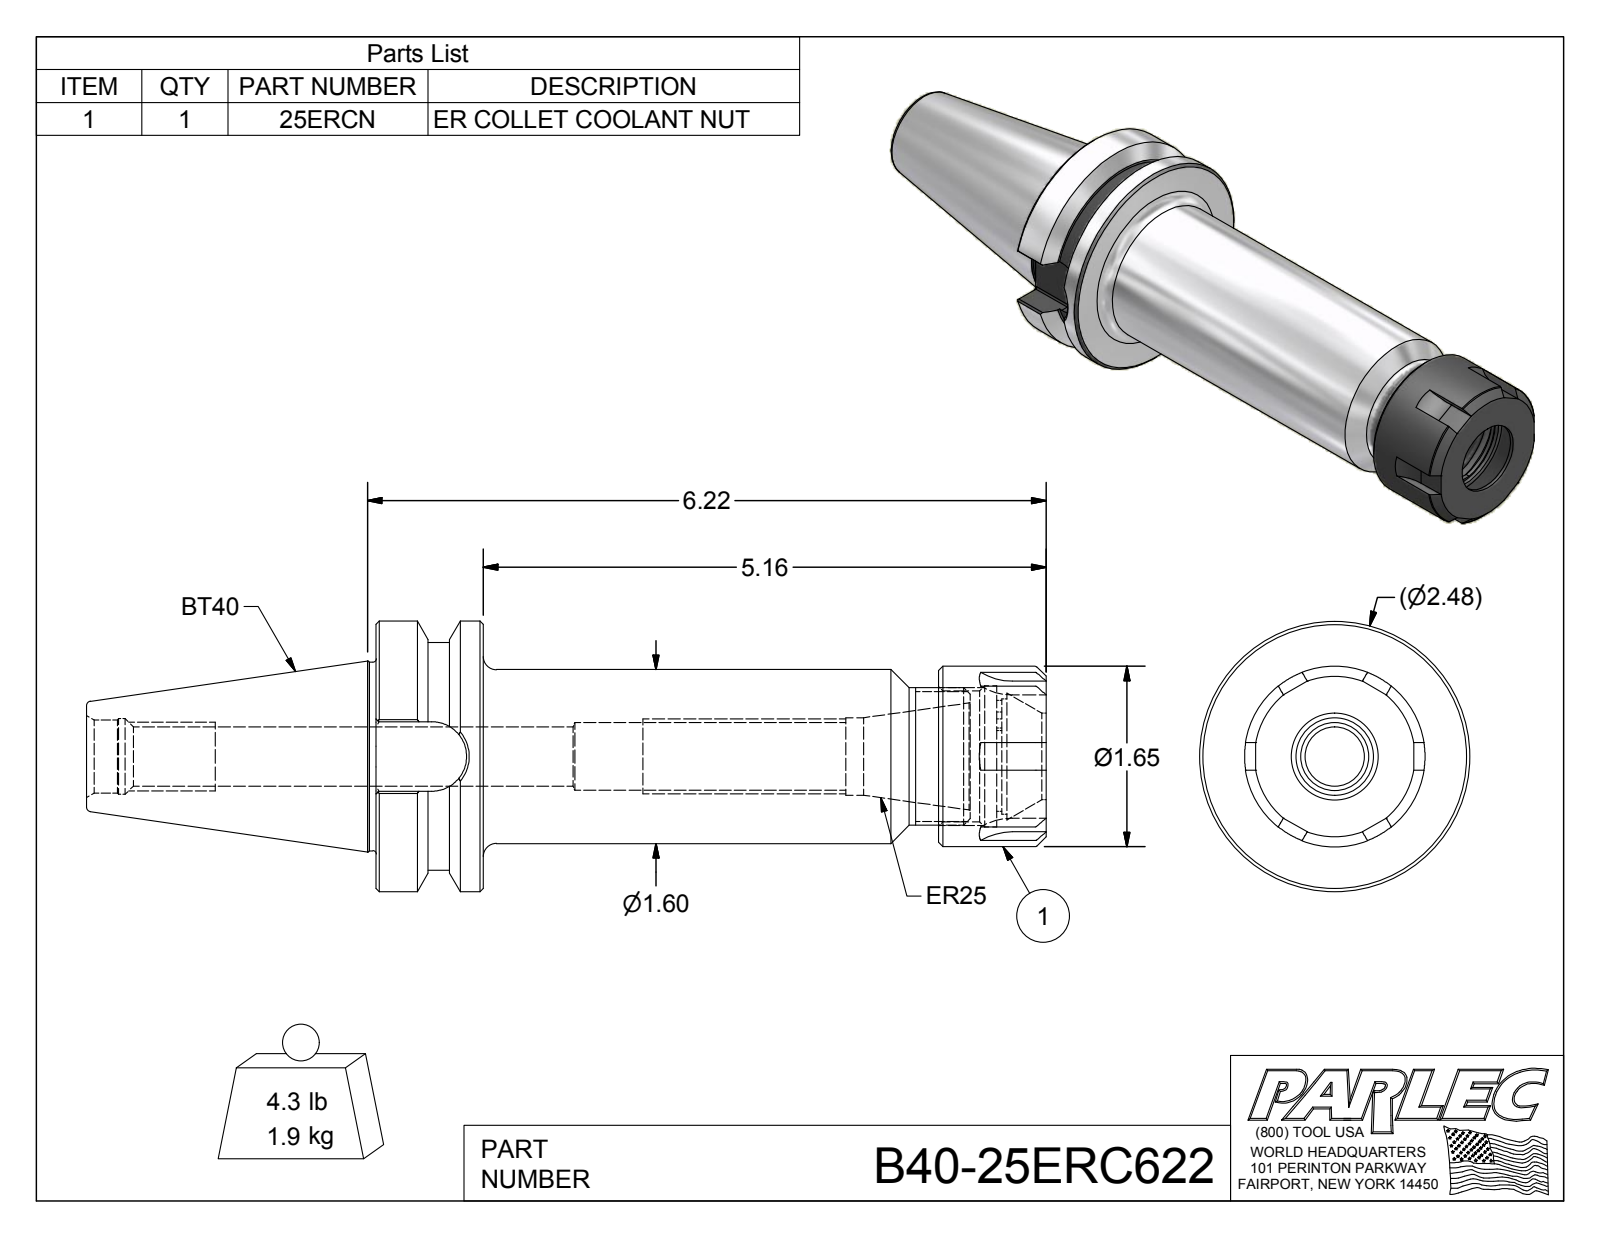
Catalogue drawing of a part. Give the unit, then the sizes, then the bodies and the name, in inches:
Units: inches
Overall size (bounding box): 8.795 × 2.48 × 2.48
Round holes (diameter × count): ⌀0.545 ×1, ⌀0.62 ×1, ⌀0.67 ×1, ⌀0.694 ×1, ⌀0.71 ×1, ⌀0.794 ×1, ⌀1.057 ×1, ⌀1.201 ×1, ⌀1.294 ×1
Round bosses / shafts (diameter × count): ⌀2.48 ×1, ⌀2.087 ×1, ⌀1.73 ×1, ⌀1.654 ×1, ⌀1.595 ×1, ⌀1.26 ×1
Partial cylindrical surfaces — rounded edges, fillets, slot ends (radius × count): R0.02 ×8, R0.5 ×6, R0.319 ×1, R0.472 ×1, R0.515 ×1
Main face-to-face distances: 0.984, 6.142, 5.158, 5.158, 4.174, 0.984, 5.689, 4.706, 0.531, 0.453
Volume: 15.2 in³ · Surface area: 76.43 in²
Bodies: 2 solids, 131 faces (52 planar, 39 cylindrical, 40 other)
Part name (STEP PRODUCT): B40-25ERC622; B40-25ER6-1; 25ERCN
STEP written by: Autodesk Inventor 2012 (AUTOMOTIVE_DESIGN)
